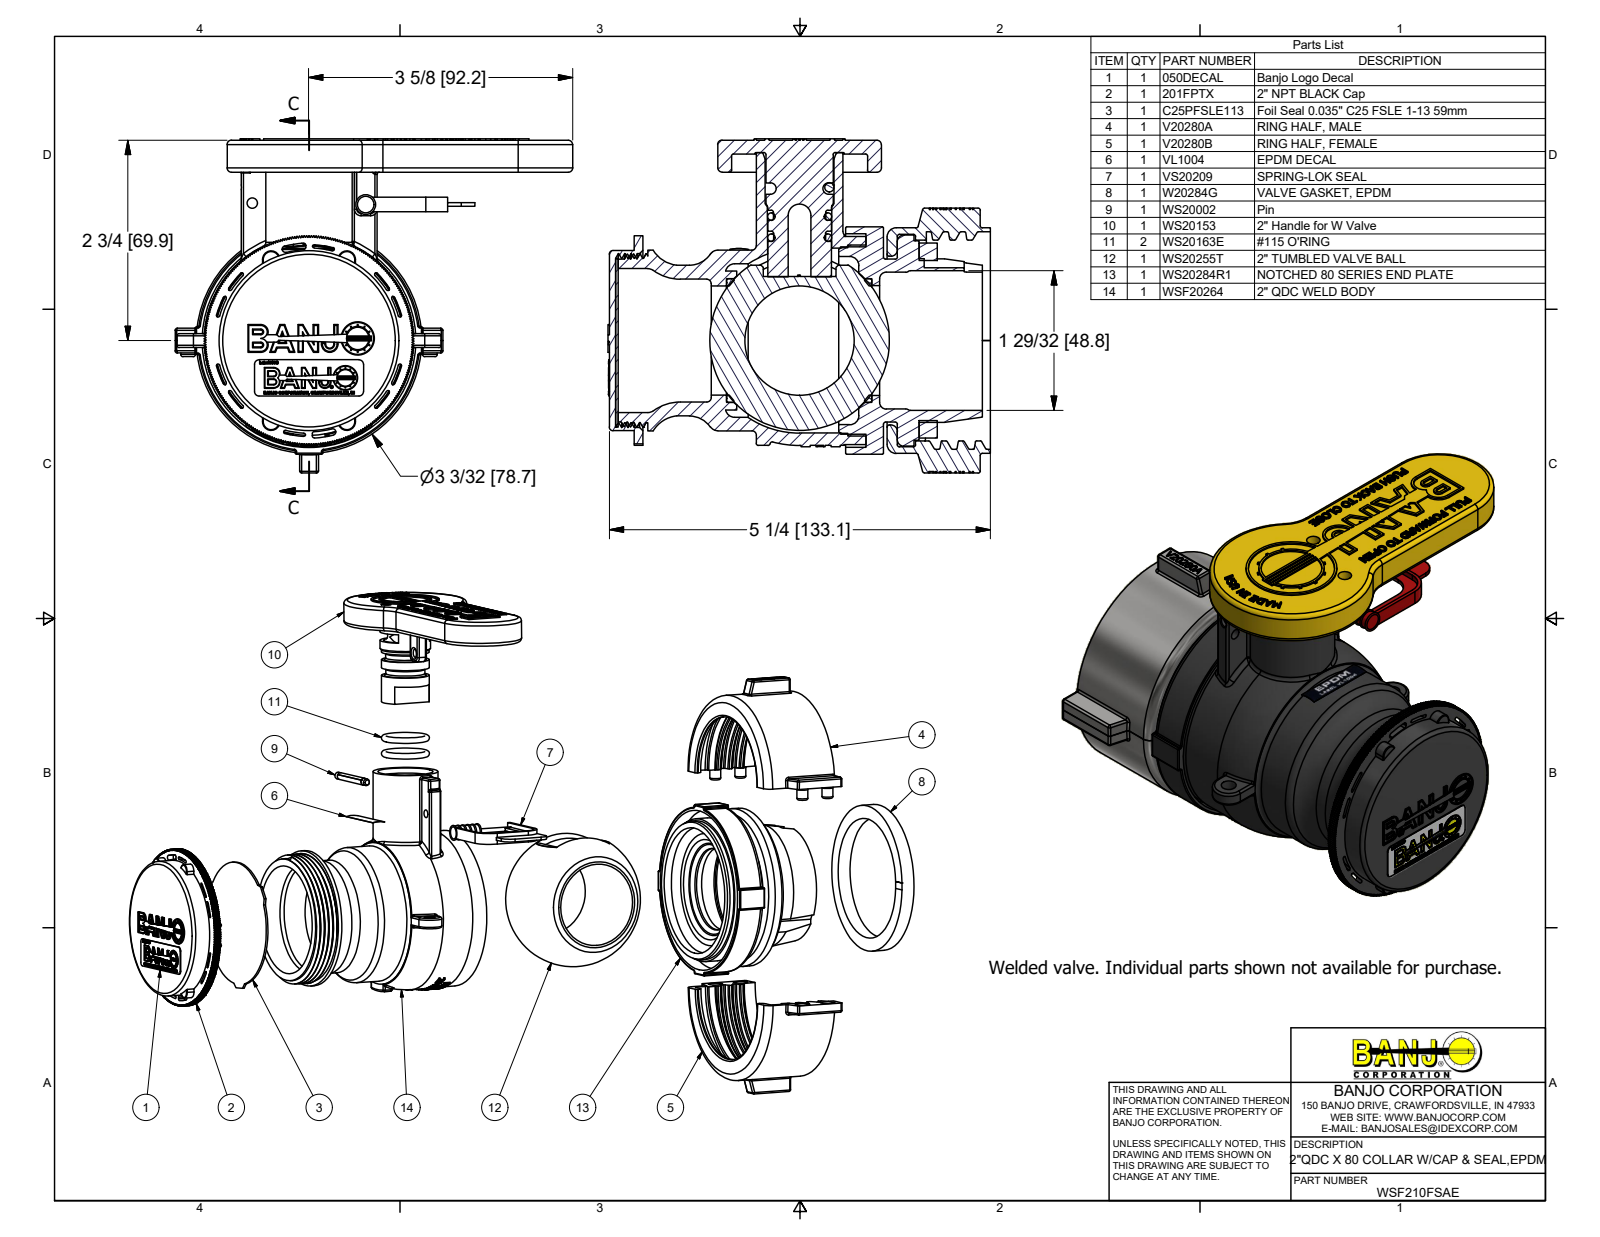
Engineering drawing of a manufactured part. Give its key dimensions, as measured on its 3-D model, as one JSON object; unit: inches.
{"part_name": "WSF210FSAE; 201FPTX; 050DECAL; C25PFSLE113 (+8 more)", "step_written_by": "Autodesk Inventor 2017 (AUTOMOTIVE_DESIGN)", "units": "inches", "bodies": {"solids": 16, "faces": 4628, "planar": 2425, "cylindrical": 976, "other": 1227}, "overall_size": [5.465, 5.259, 4.593], "volume_in3": 20.03, "surface_area_in2": 262.2, "round_holes": [[0.208, 4], [0.257, 4], [0.145, 2], [0.188, 2], [0.207, 2], [1.5, 2], [0.156, 1], [0.227, 1], [0.309, 1], [0.312, 1], [0.32, 1], [0.436, 1]], "round_bosses_or_shafts": [[0.2, 4], [2.25, 2], [3.1, 1], [3.05, 1], [2.92, 1], [2.9, 1], [2.88, 1], [2.74, 1]], "partial_cylinders_radius": [[0.03, 78], [0.016, 32], [0.06, 4], [0.063, 4], [0.118, 4], [0.069, 3], [0.225, 3], [0.01, 2]], "face_to_face_distances": [0.12, 0.19, 0.085, 0.035, 4.139, 4.174, 4.259, 0.44, 0.3, 3.839], "hole_center_spacings": [0.524, 1.562, 1.633, 2.045, 2.258, 2.515, 2.782, 2.928]}
